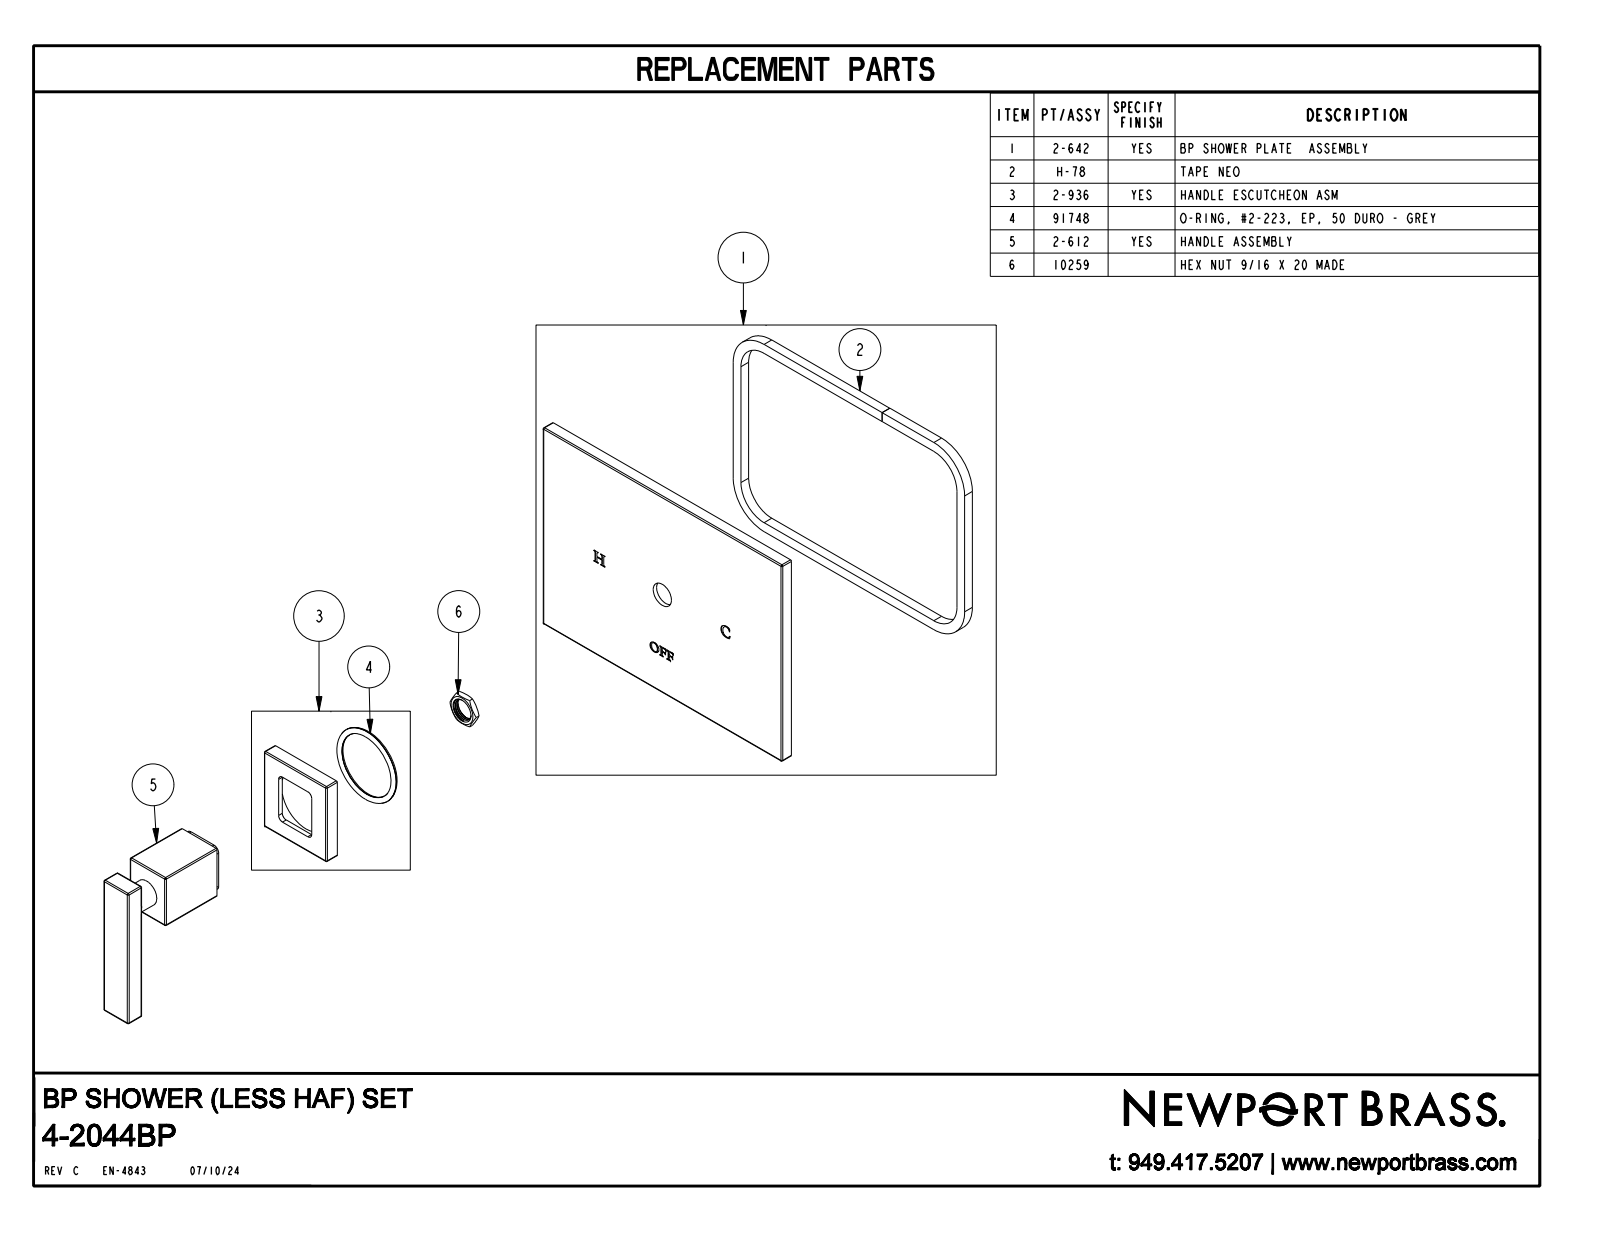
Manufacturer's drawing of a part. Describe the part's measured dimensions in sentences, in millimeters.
The part is named "4-2044BP". Its 3-D file was written by "CREO PARAMETRIC BY PTC INC, 2018400 (CONFIG_CONTROL_DESIGN)". It is 1 solid with 308 faces: 64 planar, 42 cylindrical and 202 other. Overall it measures 196.9 by 146.1 by 85.3 millimeters. Its volume is 307 900 cubic millimeters and its surface area 73 870 square millimeters. Round bosses or shafts: 1 of diameter 16.5, 1 of diameter 13.3. Partial cylindrical surfaces (rounded edges, fillets, slot ends): 36 of radius 0.8. The main face-to-face distances are 7.9, 83.7, 113.2, 88.3, 108.6, 4.6, 24.9, 85.3, 77.5, 68.6.
